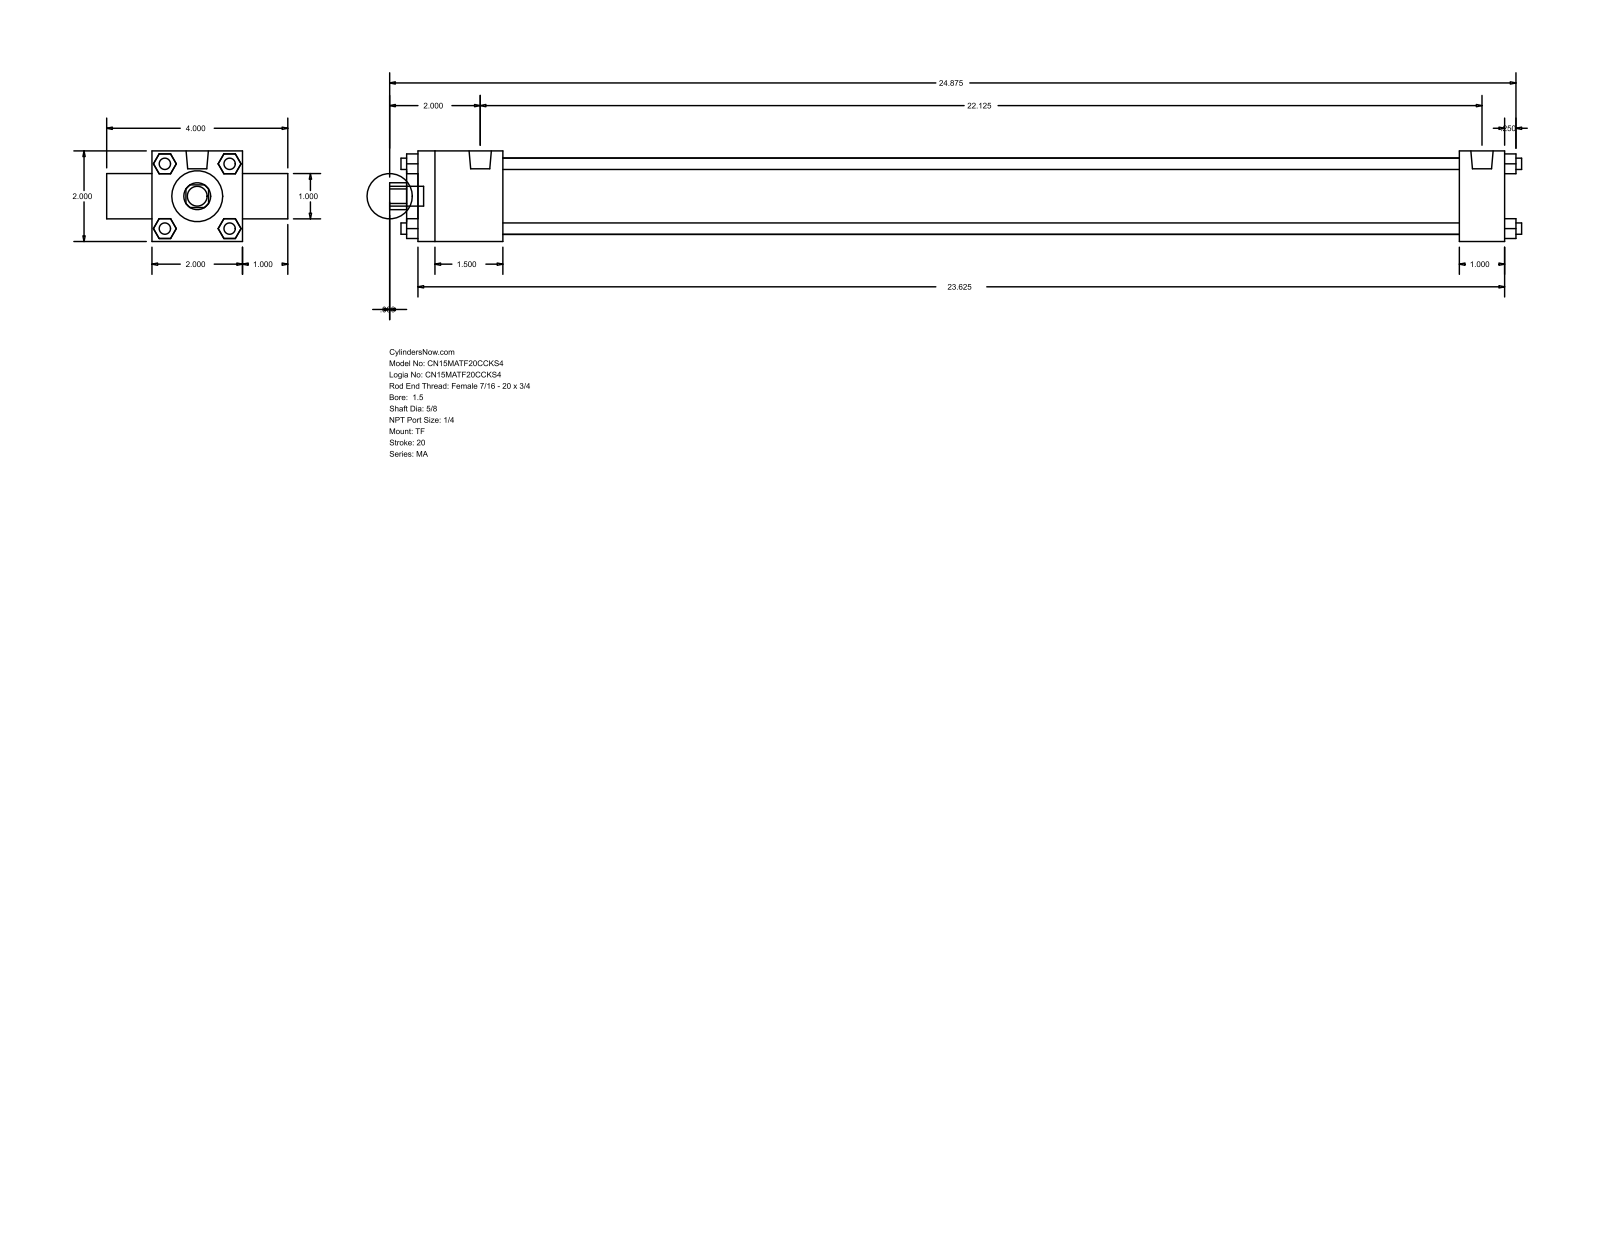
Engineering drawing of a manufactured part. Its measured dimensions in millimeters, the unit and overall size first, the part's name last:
Units: millimetres
Overall size (bounding box): 635 × 101.6 × 50.8
Round holes (diameter × count): ⌀15.88 ×1, ⌀25.4 ×1, ⌀28.57 ×1, ⌀42.93 ×1
Round bosses / shafts (diameter × count): ⌀6.35 ×4, ⌀7.94 ×3, ⌀12.49 ×2, ⌀11.11 ×1
Partial cylindrical surfaces — rounded edges, fillets, slot ends (radius × count): R7.54 ×1
Main face-to-face distances: 50.8, 25.4, 609.6, 615.95, 6.35, 76.2, 47.62, 584.2, 536.58, 561.98
Bodies: 0 solids, 120 faces (92 planar, 28 cylindrical, 0 other)
Part name (STEP PRODUCT): MA_TF__0150_0.625
STEP written by: GSSL Pune (CONFIG_CONTROL_DESIGN)
